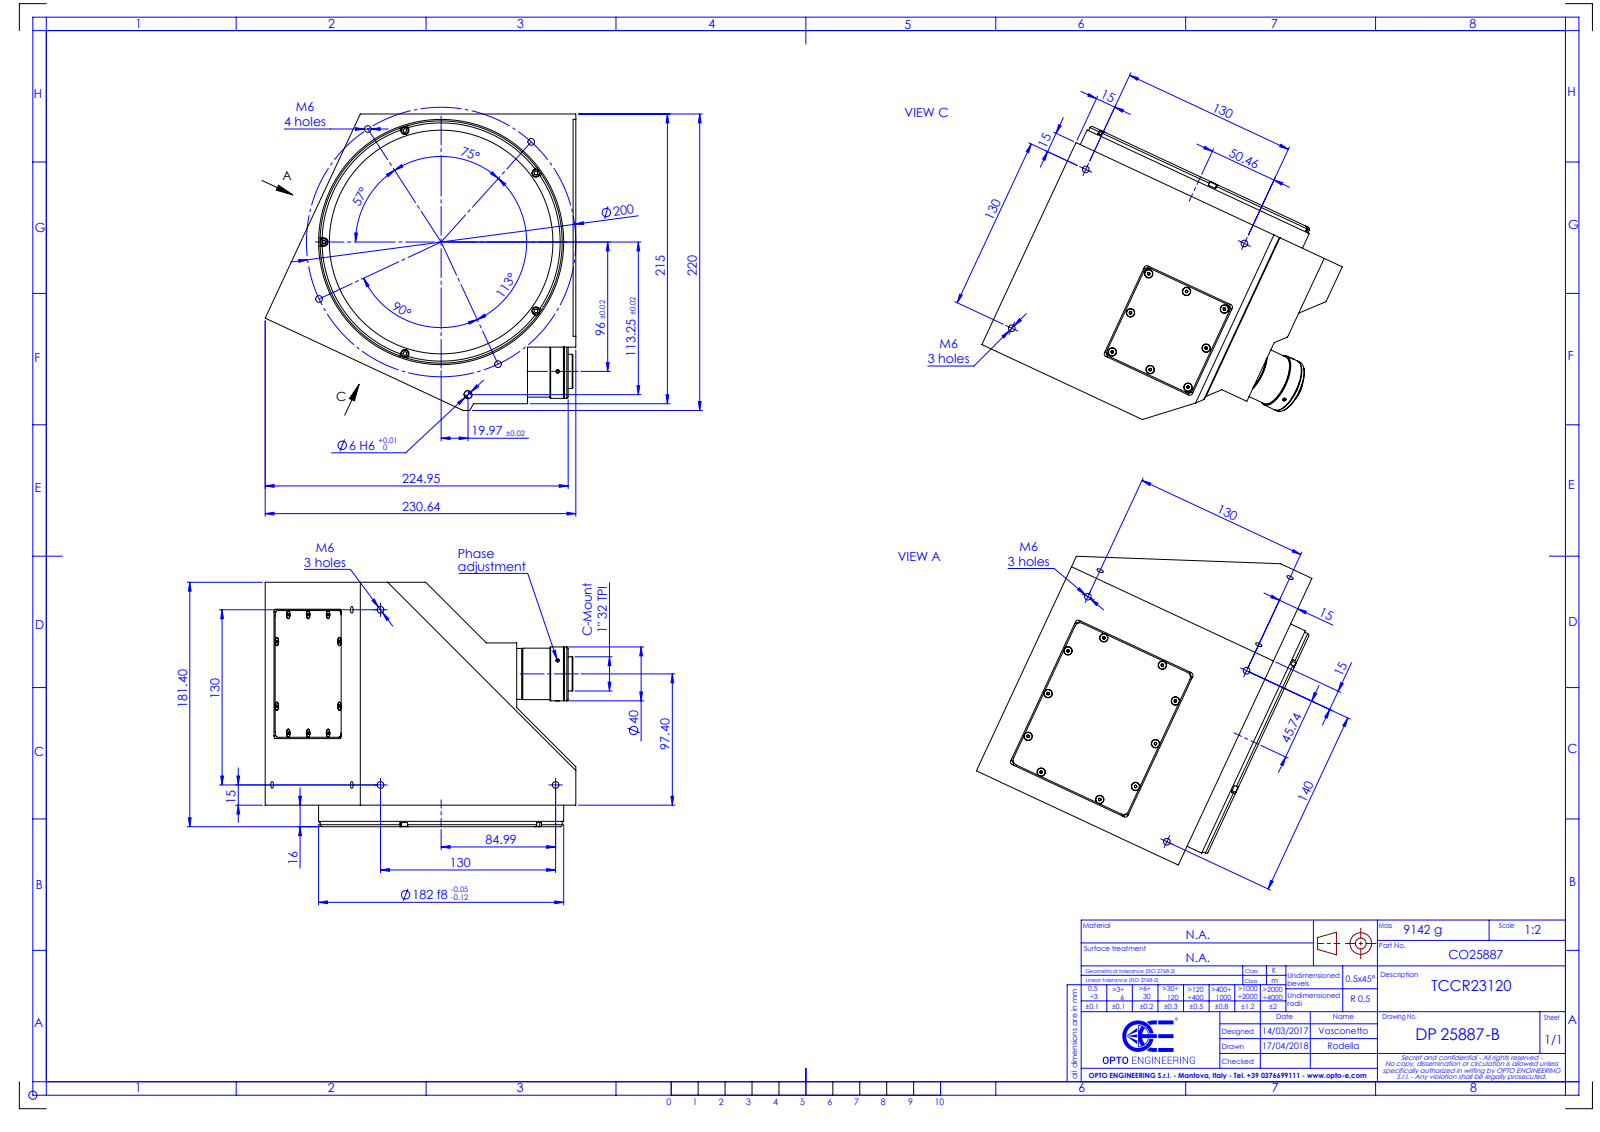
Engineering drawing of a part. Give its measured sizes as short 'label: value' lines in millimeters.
name: DP25887_TCCR23120
written by: SolidWorks 2021 (CONFIG_CONTROL_DESIGN)
unit: mm
bodies: 0 solids, 485 faces (210 planar, 138 cylindrical, 137 other)
size: 230.64 × 220 × 181.4
holes: 13× ⌀5, 1× ⌀6, 1× ⌀22, 1× ⌀22.5, 1× ⌀166, 1× ⌀170.8
bosses: 25× ⌀5.75, 5× ⌀5.5, 1× ⌀182, 1× ⌀179.8, 1× ⌀40, 1× ⌀38.2, 1× ⌀37.8, 1× ⌀25.4
rounds: 10× R4, 8× R2, 5× R3
face distances: 165.4, 0.44, 0.56, 2, 215, 165, 50, 8, 4, 19.99
hole spacings: 130, 100, 31.76, 99.99, 115, 121.75, 129.99, 131.21
